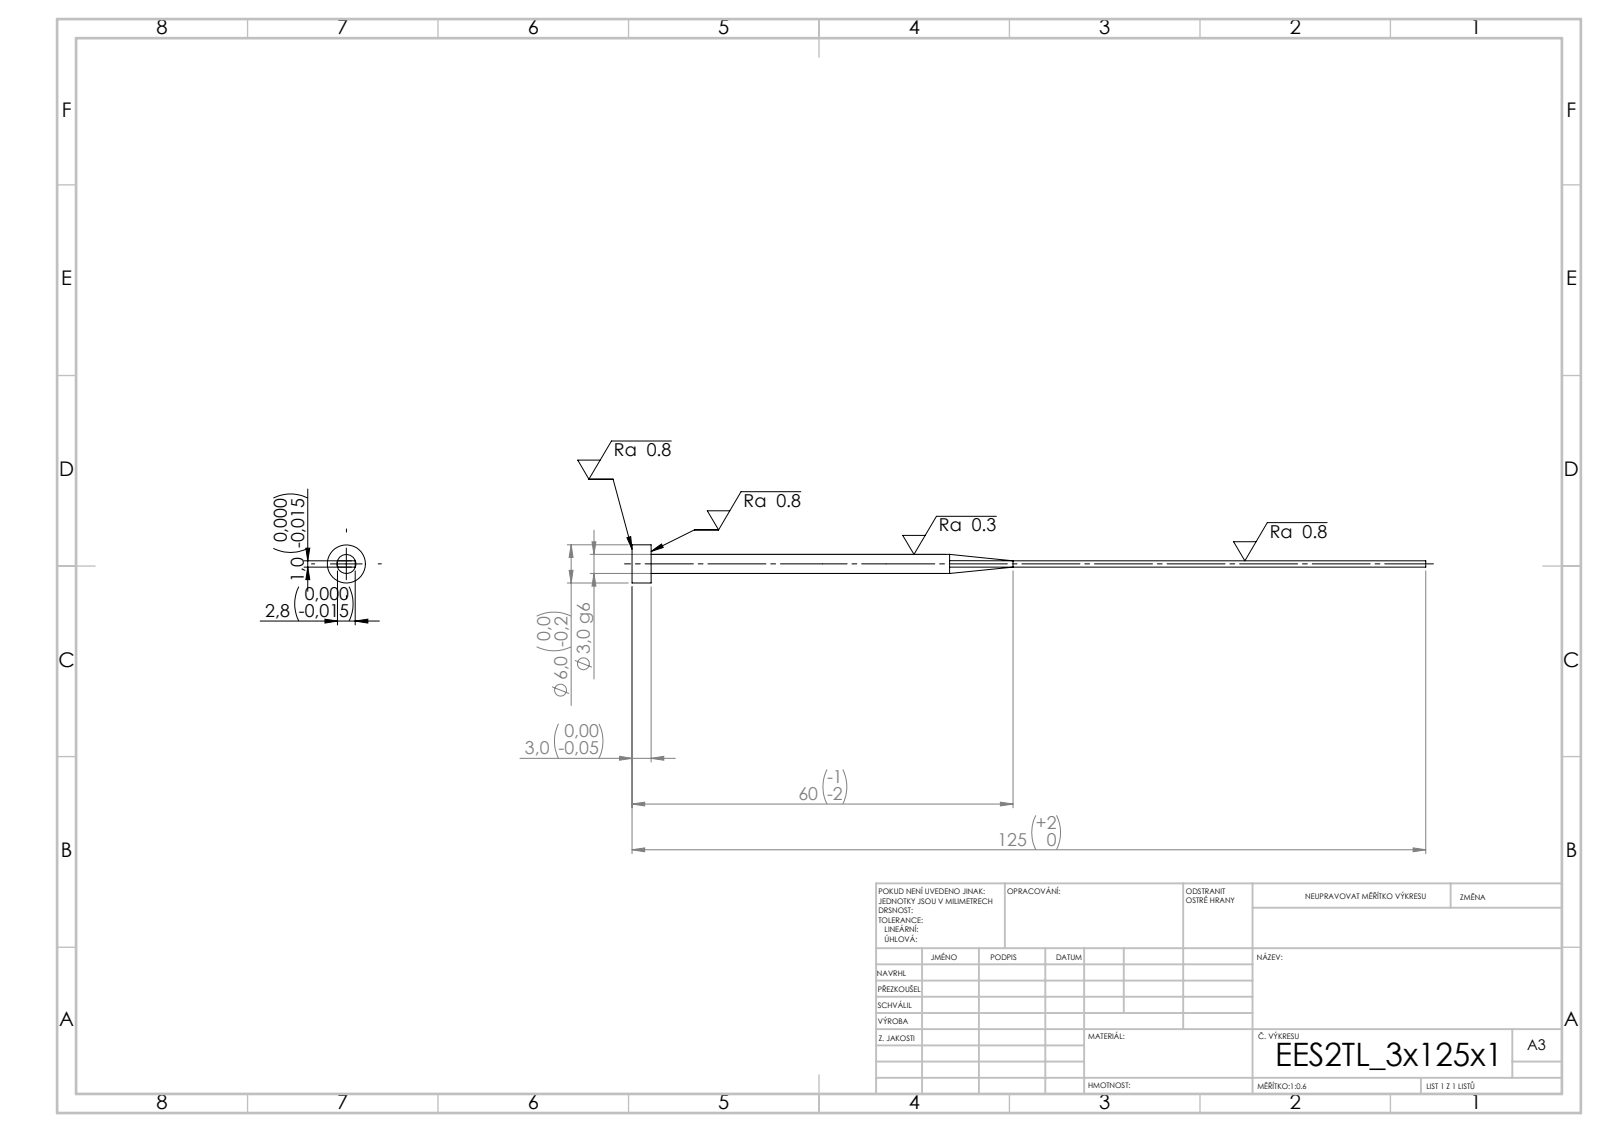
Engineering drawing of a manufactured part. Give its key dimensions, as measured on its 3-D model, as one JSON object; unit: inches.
{"step_written_by": "SolidWorks 2019 (CONFIG_CONTROL_DESIGN)", "units": "inches", "bodies": {"solids": 1, "faces": 15, "planar": 7, "cylindrical": 4, "other": 4}, "overall_size": [4.921, 0.236, 0.236], "volume_in3": 0.039, "surface_area_in2": 1.748, "round_bosses_or_shafts": [[0.236, 1], [0.118, 1]], "face_to_face_distances": [0.039, 0.11, 0.118, 4.921, 4.803]}
